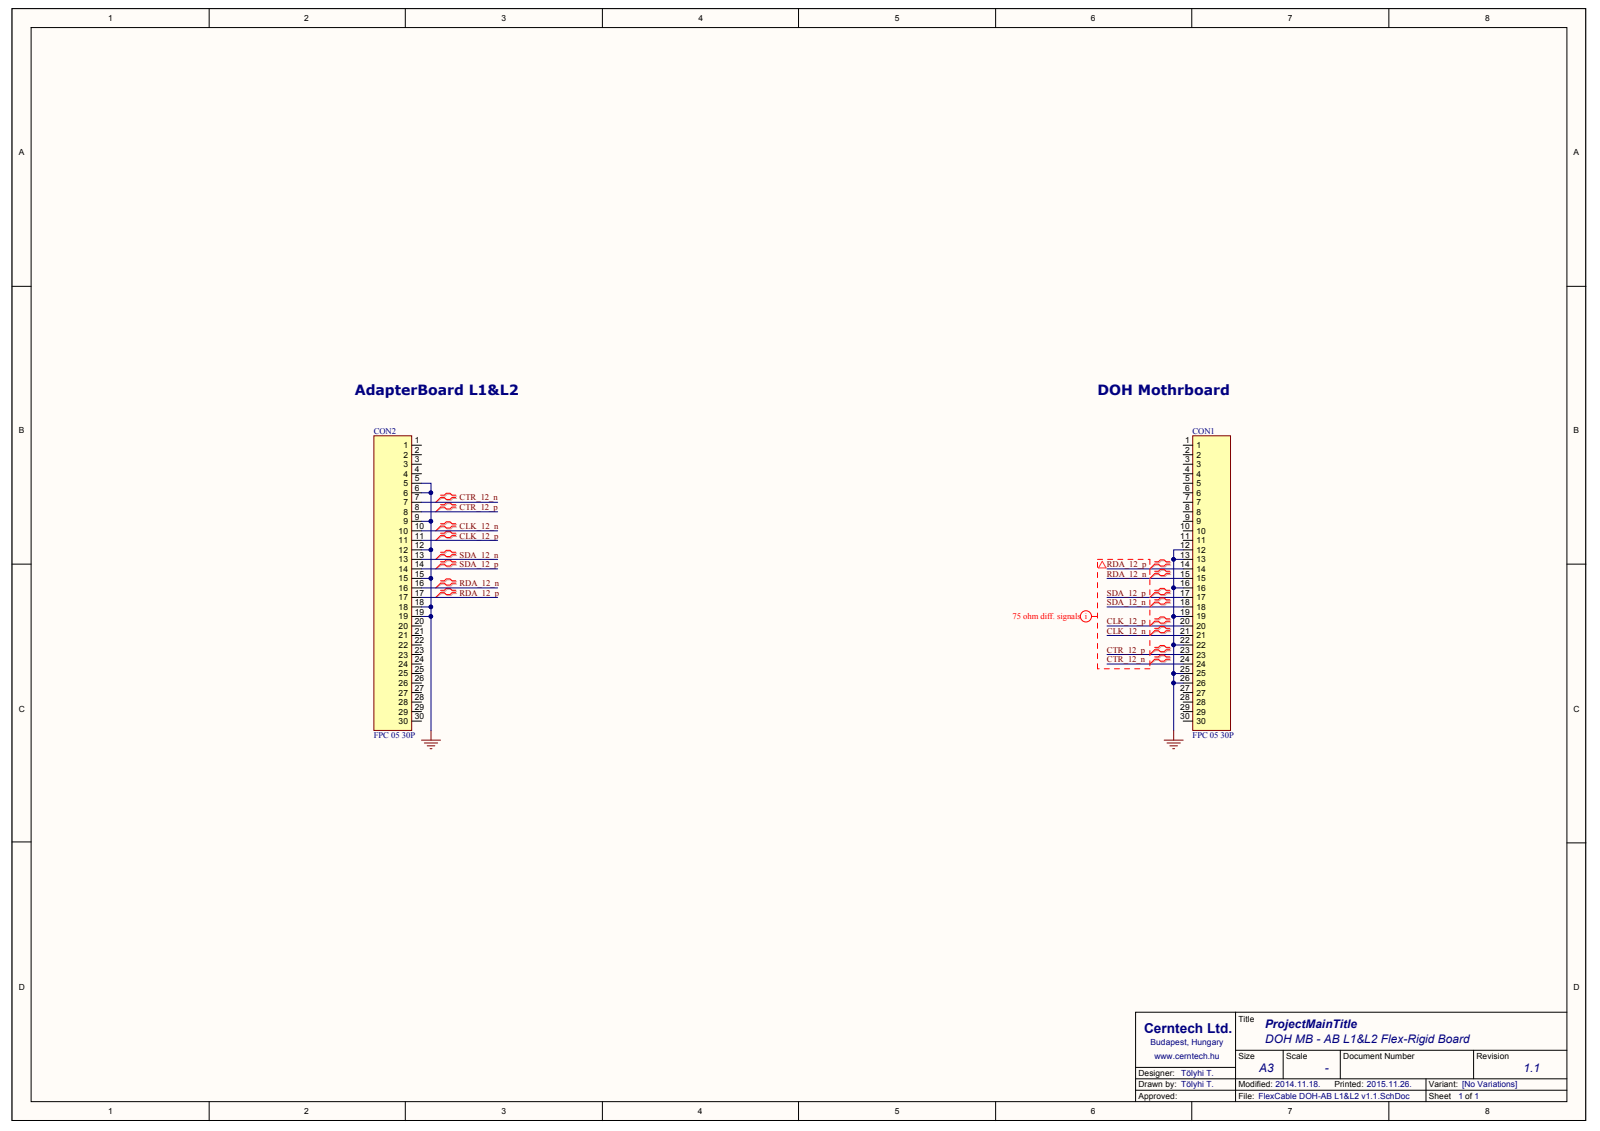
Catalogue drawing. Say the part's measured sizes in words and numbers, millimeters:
The part is named "PCB; BoardFC_DOH_L1&L2_v1.1.3". Its 3-D file was written by "Open CASCADE 6.5 (AUTOMOTIVE_DESIGN_CC2)". It is 11 solids with 144 faces: 144 planar, 0 cylindrical and 0 other. Overall it measures 177.01 by 16.61 by 0.23 millimeters. Its volume is 374 cubic millimeters and its surface area 5 597 square millimeters. The main face-to-face distances are 15.5, 3.14, 47.37, 1.58, 8, 5, 172, 44.23, 50.51, 167.
